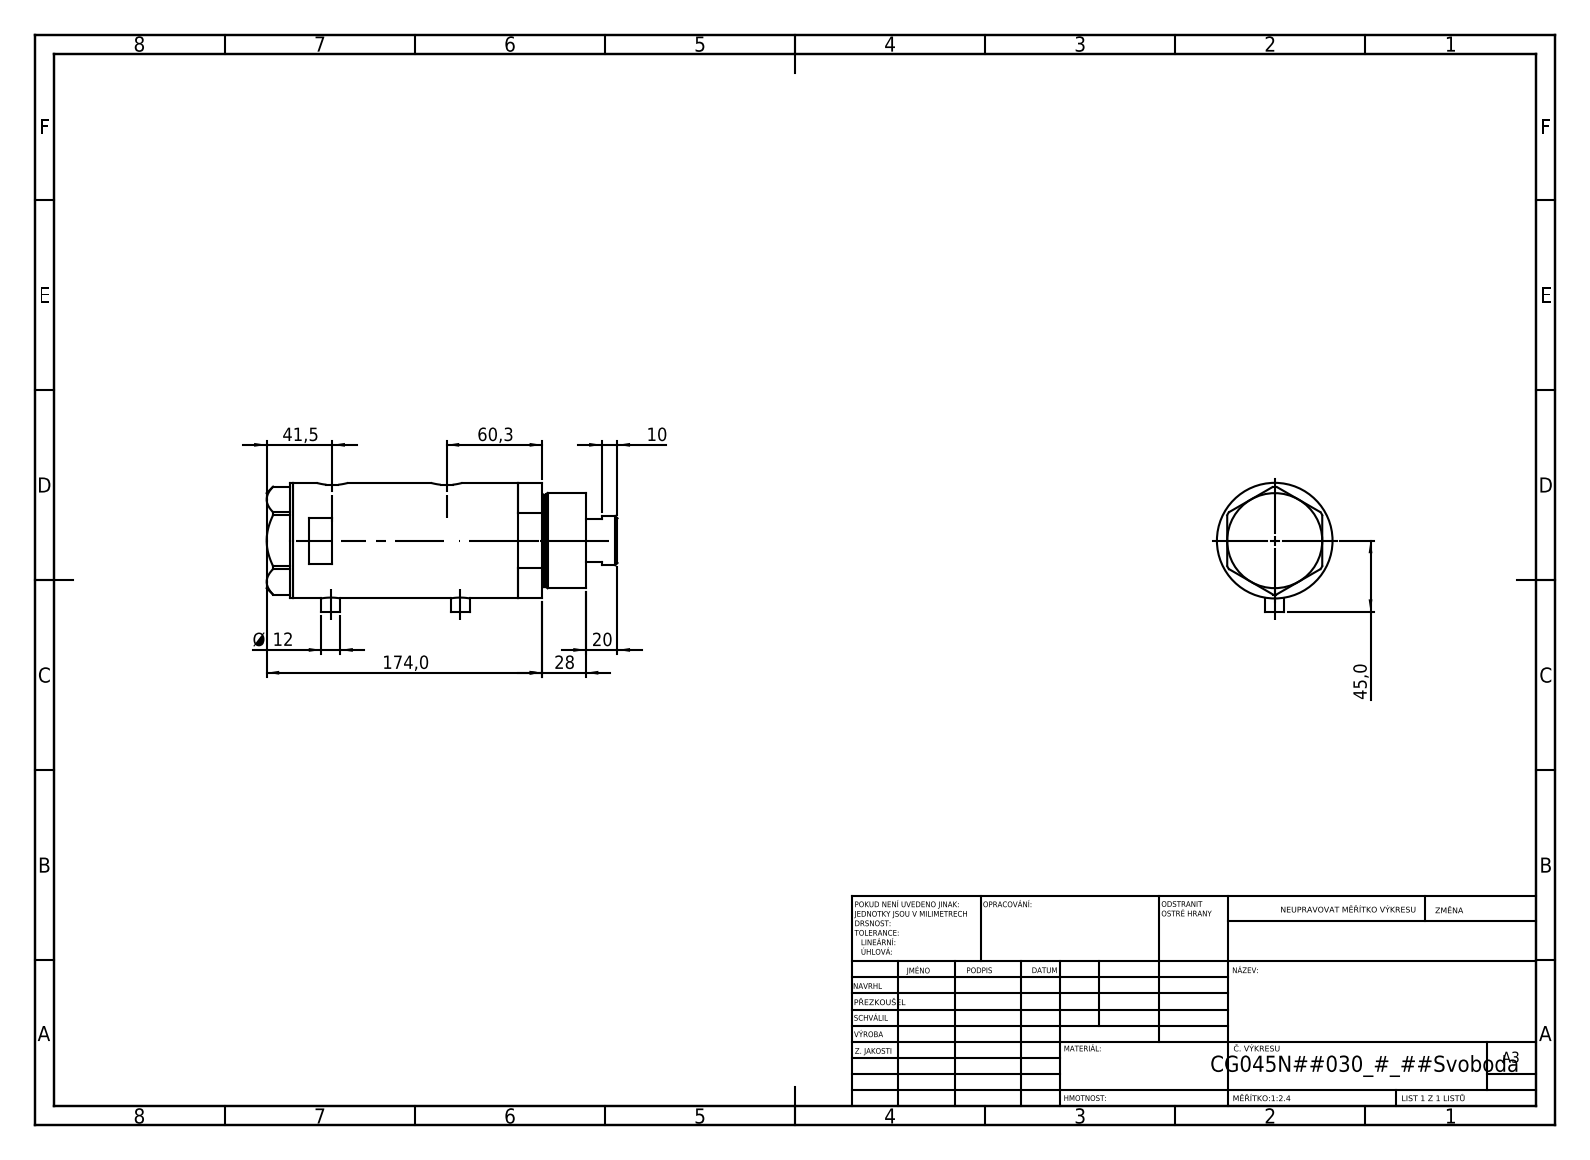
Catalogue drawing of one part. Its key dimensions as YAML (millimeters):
part_name: "V270CG_MIDDLE; V270CG_FRONT; V270CG_BACK; V270CG_VC"
step_written_by: "SolidWorks 2019 (CONFIG_CONTROL_DESIGN)"
units: millimeters
bodies: {solids: 4, faces: 125, planar: 50, cylindrical: 55, other: 20}
overall_size: [221.52, 81.5, 73]
volume: 770115
surface_area: 134868
round_holes:
  - {diameter: 5, count: 2}
  - {diameter: 12.5, count: 2}
  - {diameter: 13.16, count: 2}
  - {diameter: 10.5, count: 1}
  - {diameter: 32, count: 1}
  - {diameter: 33.5, count: 1}
  - {diameter: 45, count: 1}
  - {diameter: 48, count: 1}
  - {diameter: 64, count: 1}
round_bosses_or_shafts:
  - {diameter: 12, count: 2}
  - {diameter: 73, count: 1}
  - {diameter: 60, count: 1}
  - {diameter: 58, count: 1}
  - {diameter: 31, count: 1}
partial_cylinders:
  - {radius: 10, count: 2}
face_to_face_distances: [97.14, 16.5, 113.64, 2, 185.01, 201.51, 87.87, 42.5, 26, 71.14]
hole_center_spacings: [81.65, 0.99, 1, 8.5, 8.51, 72.15, 73.14, 73.15]
